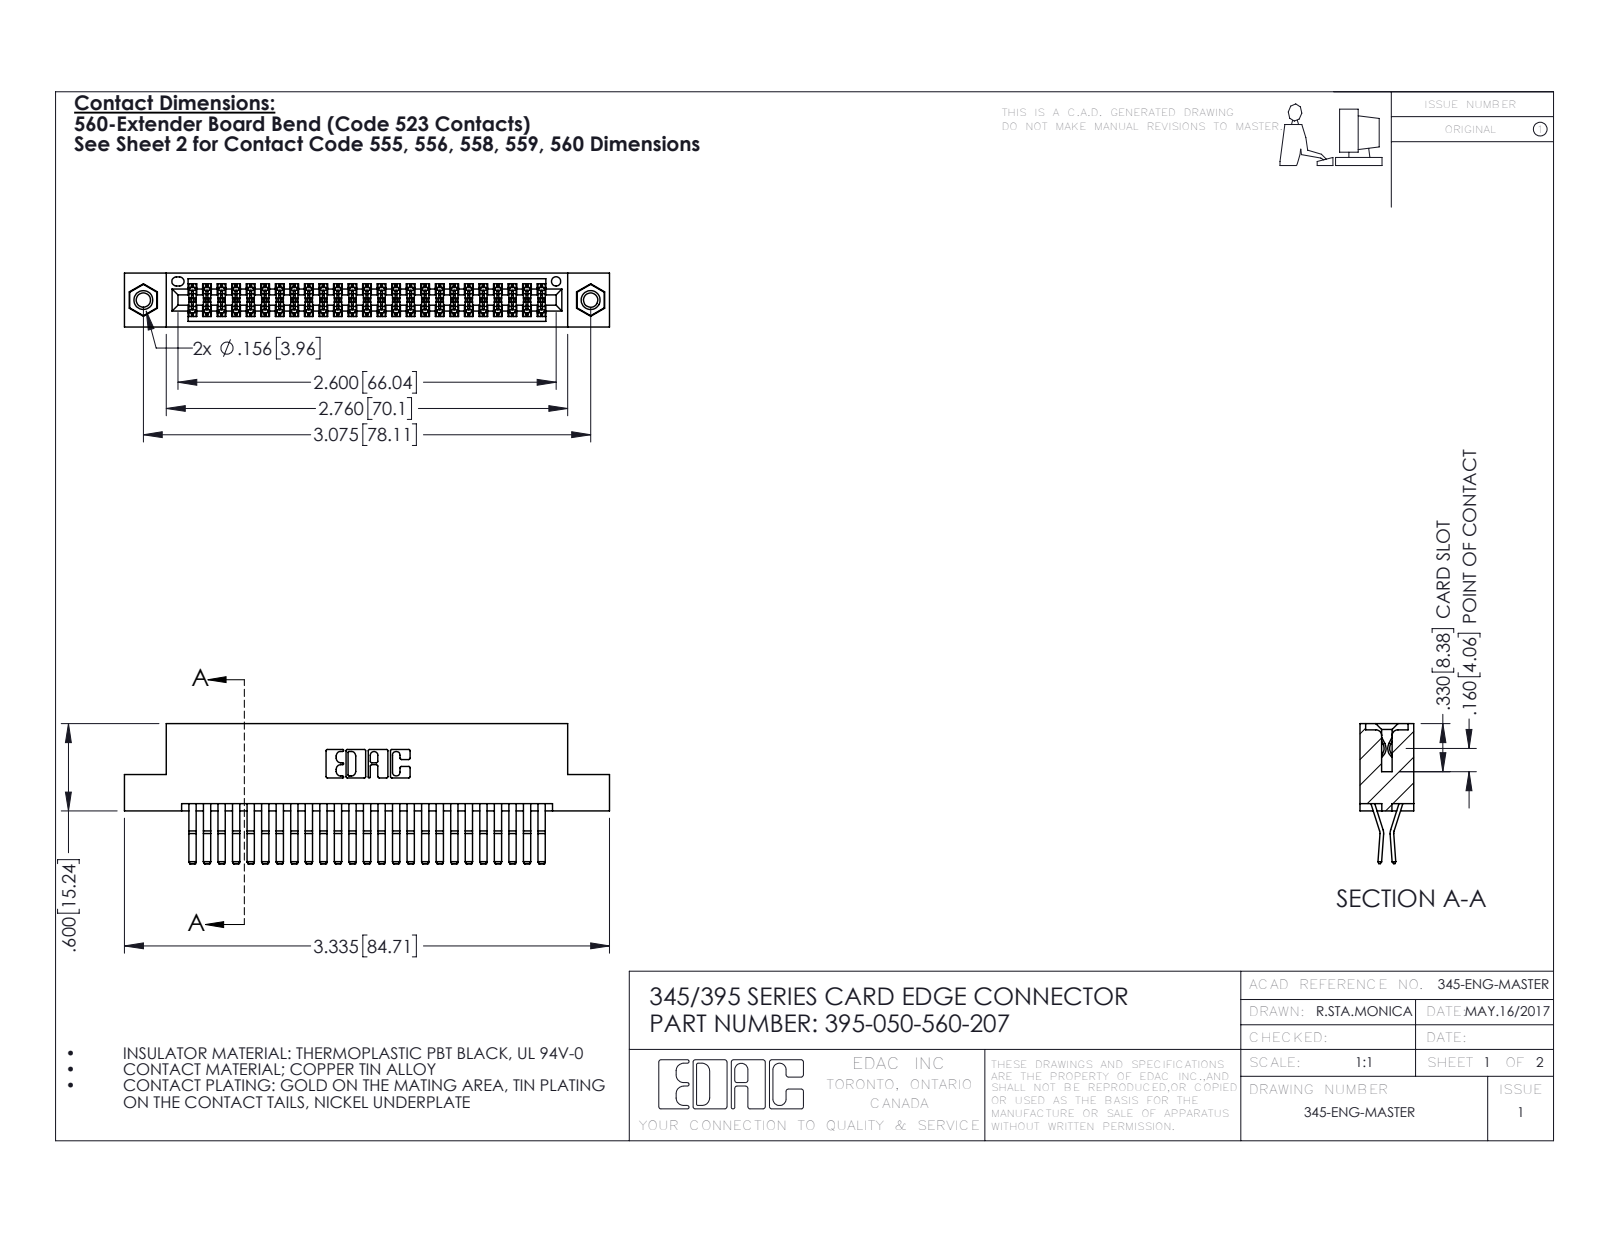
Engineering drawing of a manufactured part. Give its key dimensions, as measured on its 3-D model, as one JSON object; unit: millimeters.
{"part_name": "345-292-001_560 Tail; 345 Part_Flush Mounting Lugs - 0.156 Dia-TI; 395-050-560-207; 345-250-001_345-250-005-103", "step_written_by": "SolidWorks 2016 (CONFIG_CONTROL_DESIGN)", "units": "millimeters", "bodies": {"solids": 53, "faces": 2786, "planar": 1762, "cylindrical": 1008, "other": 16}, "overall_size": [84.7, 24.4, 9.4], "volume_mm3": 8390, "surface_area_mm2": 12940, "round_holes": [[2.5, 2], [3.2, 2], [4, 2], [1.6, 1]], "round_bosses_or_shafts": [[3.9, 2]], "partial_cylinders_radius": [[0.2, 75], [0.3, 22], [0.2, 6], [0.8, 6], [0.7, 3], [0.3, 2], [0.4, 2], [0.5, 2]], "face_to_face_distances": [0.6, 1.8, 7.6, 5.1, 9.4, 2.5, 6.9, 5.7, 4.4, 3.8], "hole_center_spacings": [6.9, 72.1, 78.1]}
